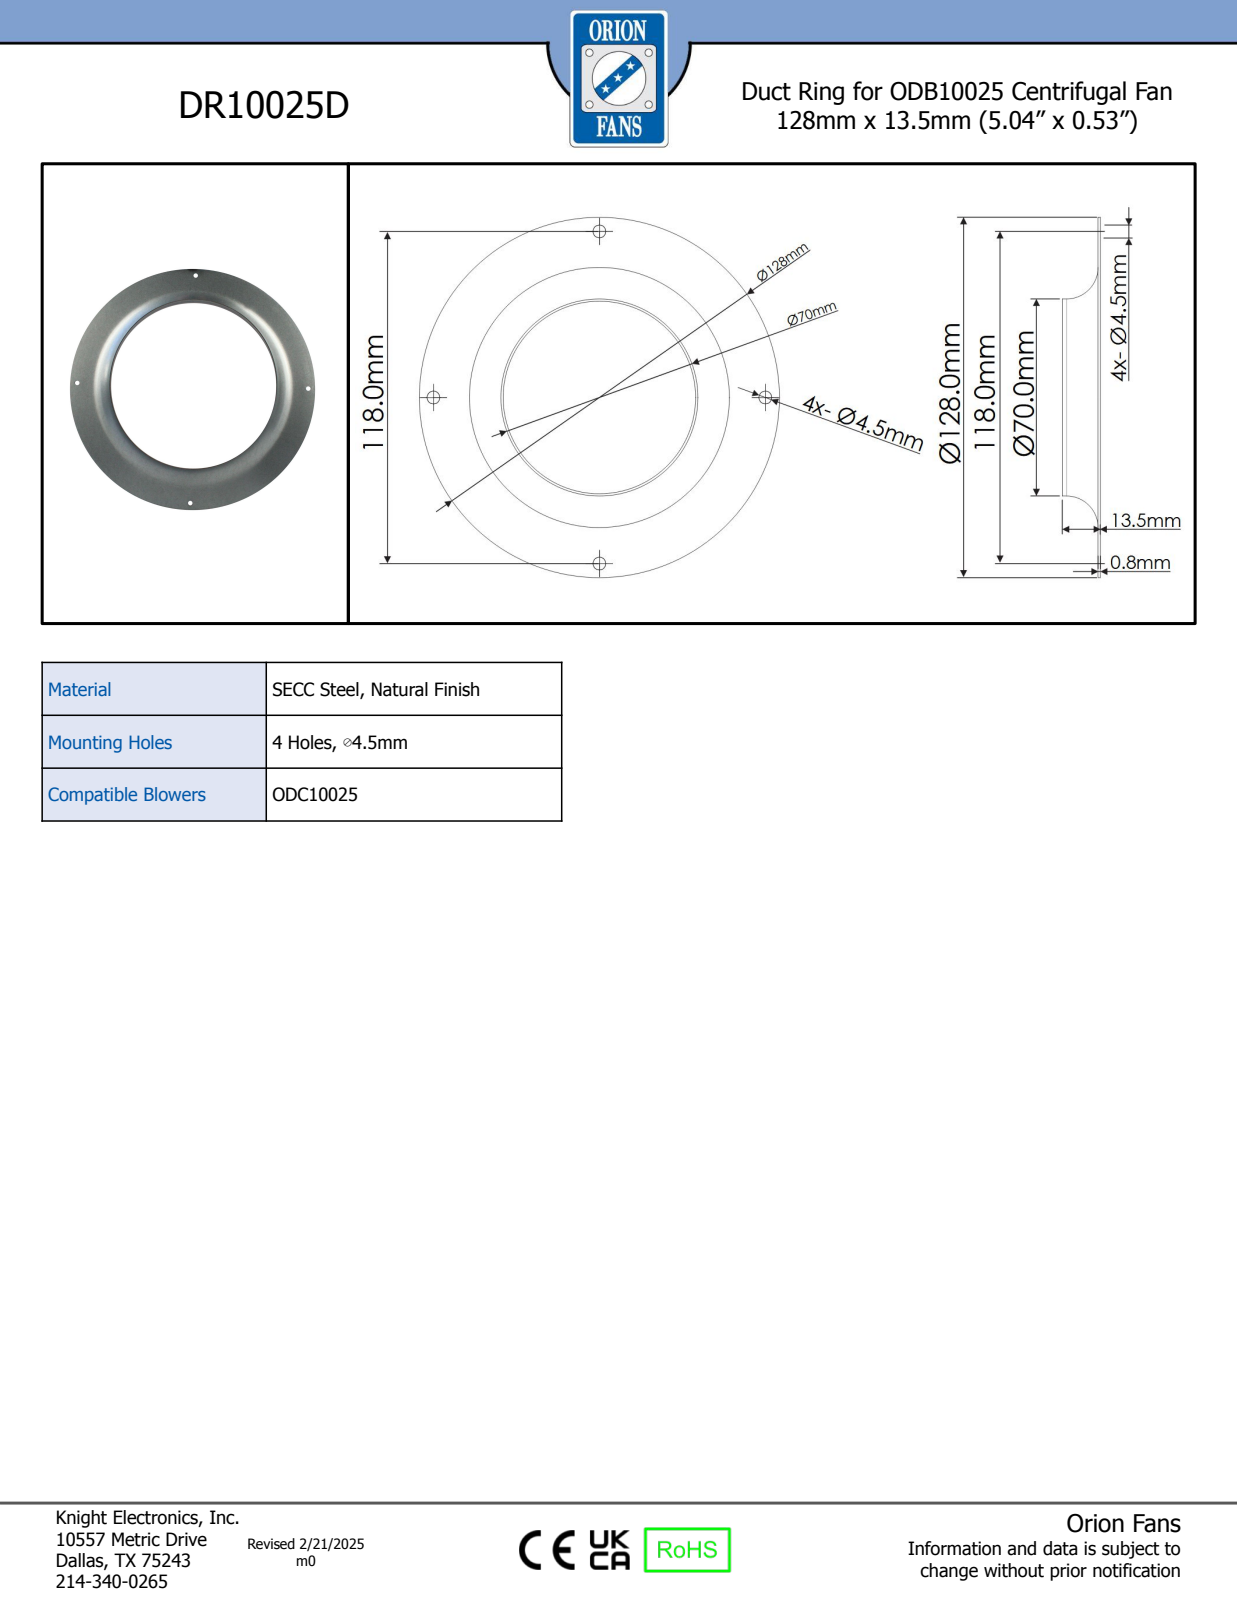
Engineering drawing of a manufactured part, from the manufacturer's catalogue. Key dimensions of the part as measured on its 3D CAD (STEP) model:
Part name (STEP PRODUCT): DR10025D
STEP written by: SolidWorks 2018 (CONFIG_CONTROL_DESIGN)
Units: millimetres
Bodies: 1 solid, 21 faces (3 planar, 14 cylindrical, 4 other)
Overall size (bounding box): 128 × 128 × 13.5
Volume: 8 695 mm³ · Surface area: 22 276 mm²
Round holes (diameter × count): ⌀4.5 ×4, ⌀68.4 ×1
Round bosses / shafts (diameter × count): ⌀128 ×1, ⌀70 ×1
Main face-to-face distances: 0.8, 13.5, 12.7
Hole centre spacings: 59, 83.44, 118
